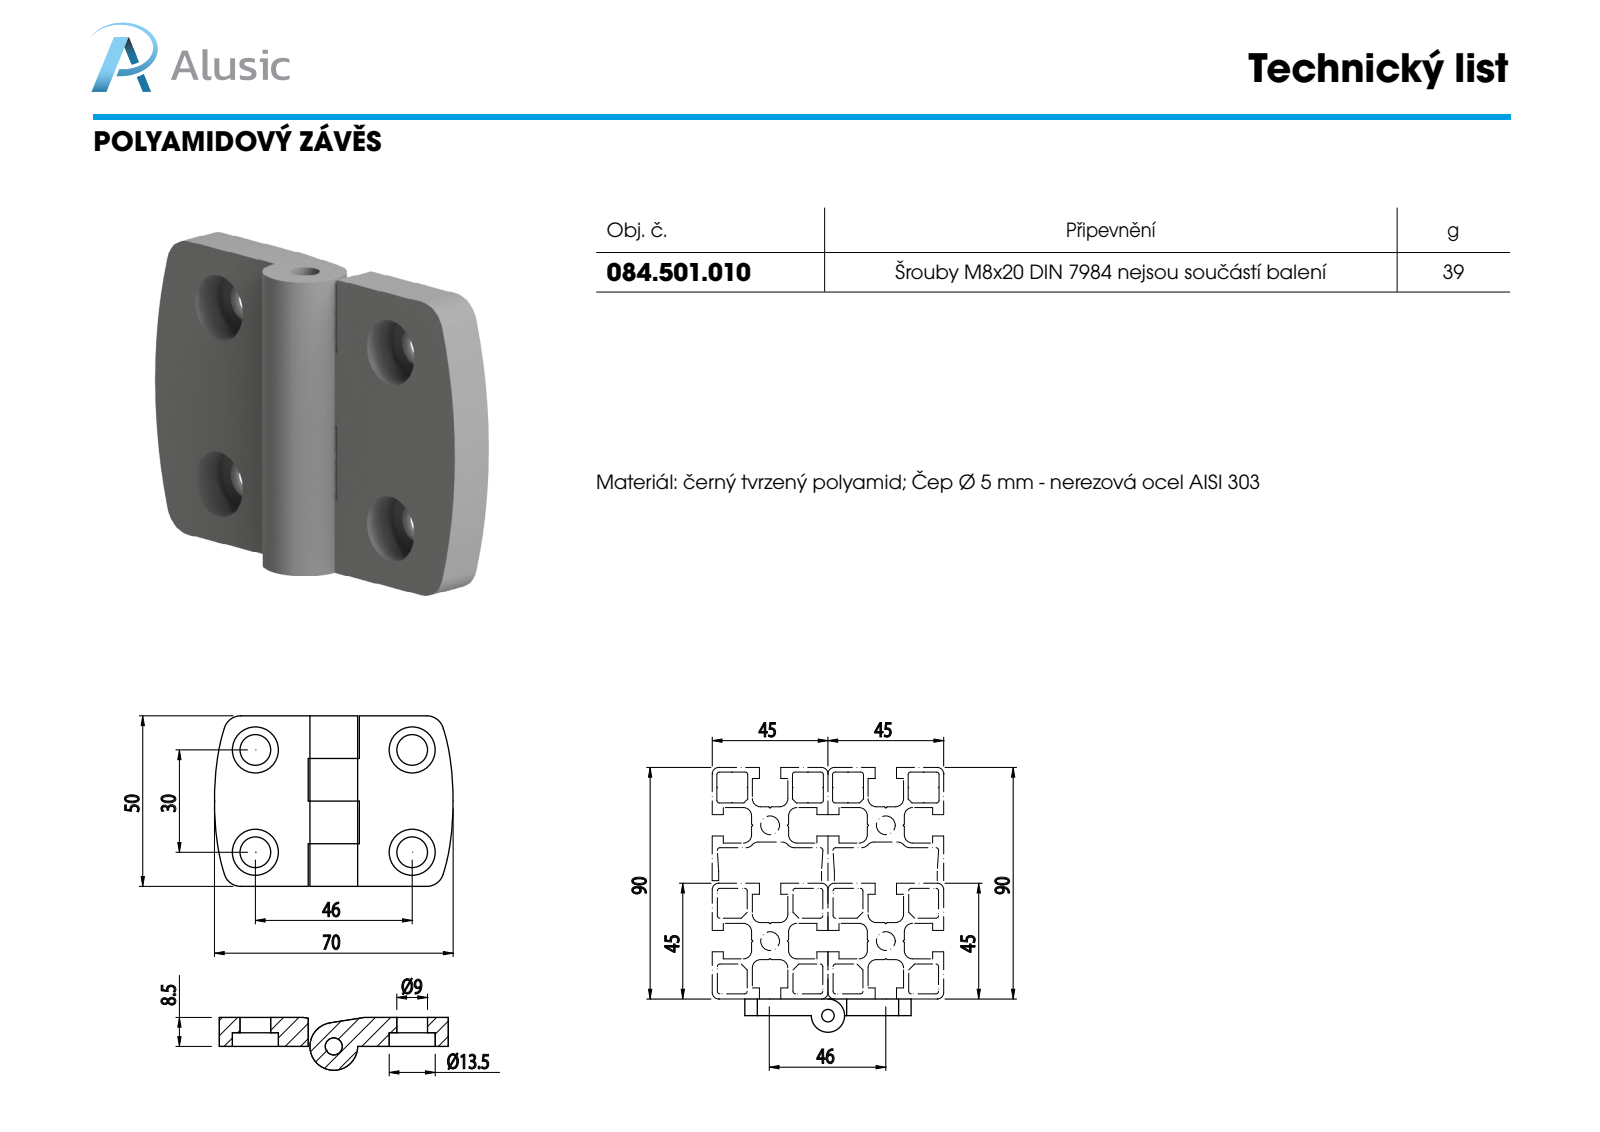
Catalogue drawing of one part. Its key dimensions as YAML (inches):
part_name: "084.501.010; 084.501.010 ALETTA"
step_written_by: "SolidWorks 2011 (CONFIG_CONTROL_DESIGN)"
units: inches
bodies: {solids: 2, faces: 58, planar: 24, cylindrical: 34, other: 0}
overall_size: [2.756, 1.969, 0.61]
volume: 1.61
surface_area: 18.6
round_holes:
  - {diameter: 0.354, count: 4}
  - {diameter: 0.531, count: 4}
  - {diameter: 0.197, count: 1}
round_bosses_or_shafts:
  - {diameter: 0.551, count: 1}
partial_cylinders:
  - {radius: 0.197, count: 4}
  - {radius: 3.15, count: 2}
face_to_face_distances: [0.335, 0.492, 0.984, 1.476, 1.969, 0.177, 0.157, 0.591]
hole_center_spacings: [1.181, 1.811, 2.162]
